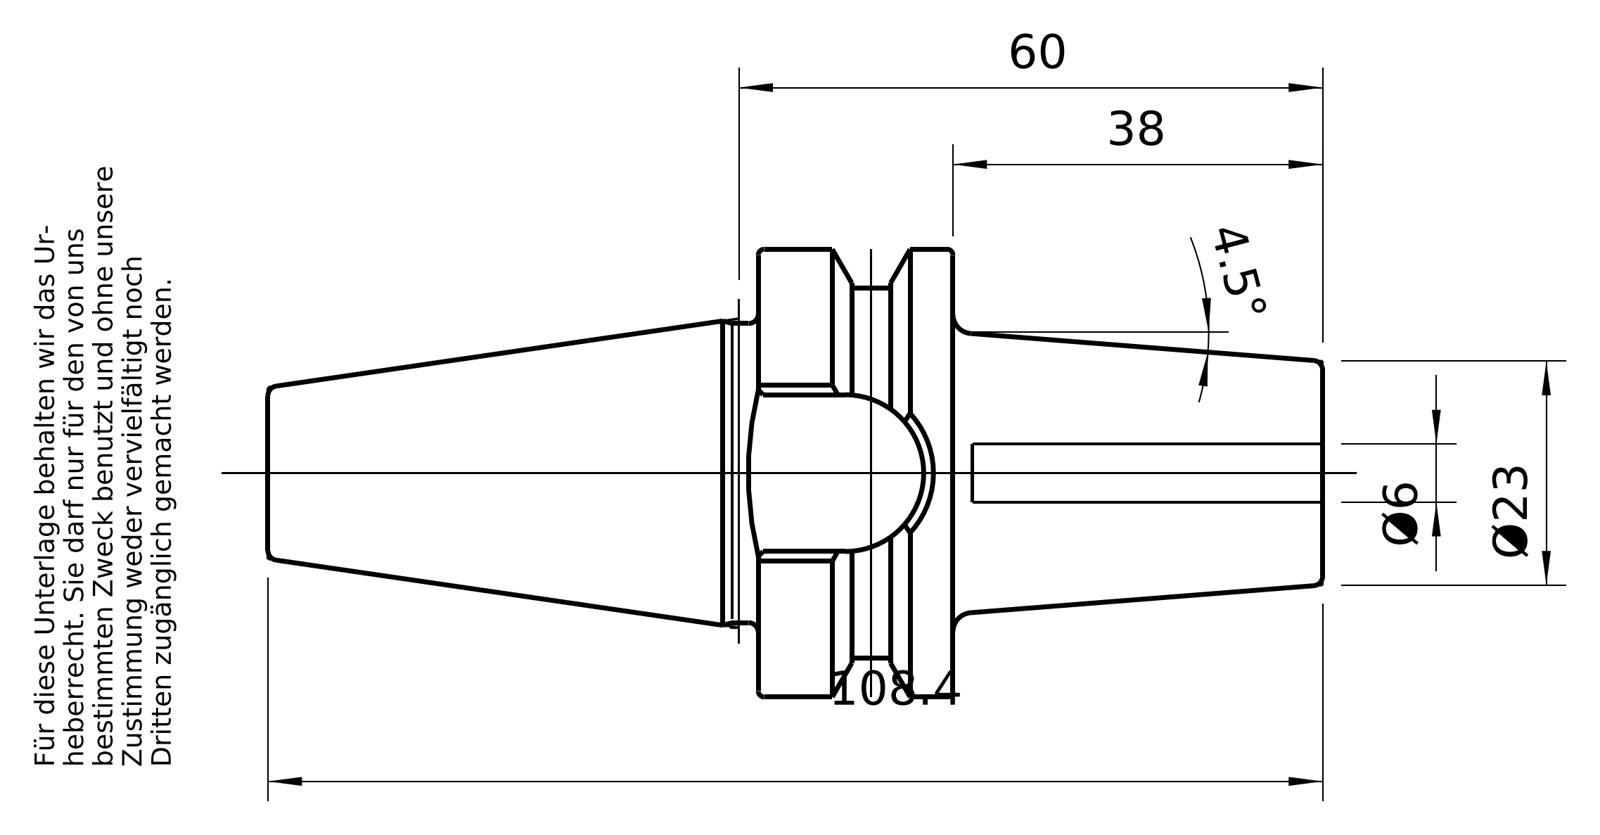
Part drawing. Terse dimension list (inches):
name: 30-645-06
written by: PRO/ENGINEER BY PARAMETRIC TECHNOLOGY CORPORATION, 2010430 (CONFIG_CONTROL_DESIGN)
unit: in
bodies: 1 solid, 94 faces (26 planar, 20 cylindrical, 48 other)
size: 4.268 × 1.81 × 1.81
volume: 4.199 in³; area: 23.72 in²
holes: 1× ⌀0.236, 1× ⌀0.398, 1× ⌀0.493, 1× ⌀0.512
bosses: 1× ⌀1.81, 1× ⌀1.211, 1× ⌀0.473
rounds: 1× R0.319, 1× R0.743
face distances: 0.787, 2.283, 1.496, 1.272, 0.638, 1.984, 2.772, 4.268, 0.984, 1
